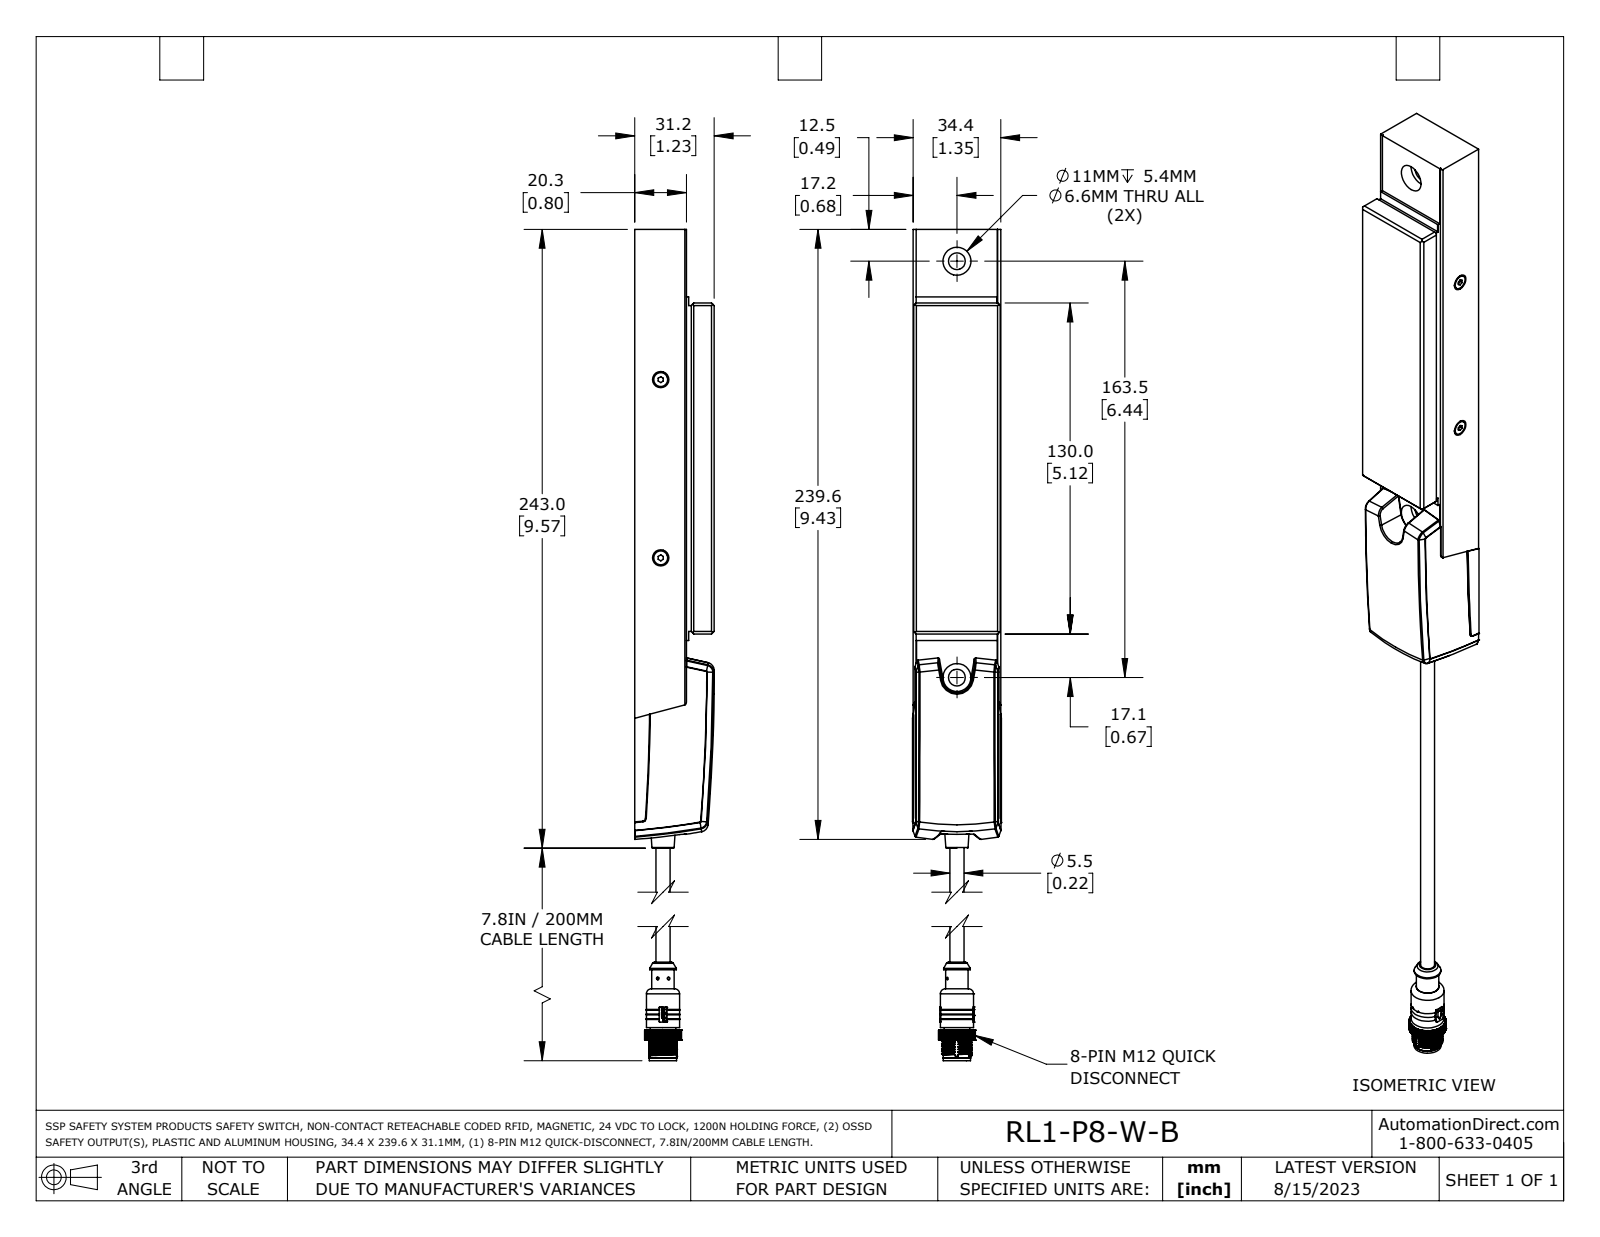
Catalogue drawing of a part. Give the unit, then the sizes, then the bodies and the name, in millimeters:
Units: millimetres
Overall size (bounding box): 434.1 × 34.9 × 31.2
Round holes (diameter × count): ⌀1 ×2, ⌀6.6 ×2, ⌀11 ×2, ⌀2.9 ×1, ⌀8.3 ×1
Round bosses / shafts (diameter × count): ⌀0.8 ×8, ⌀5.5 ×5, ⌀13 ×1, ⌀10.7 ×1, ⌀10.7 ×1, ⌀10.5 ×1, ⌀10 ×1, ⌀9.5 ×1
Partial cylindrical surfaces — rounded edges, fillets, slot ends (radius × count): R0.2 ×9, R0.2 ×4, R0.2 ×3, R0.6 ×3, R800 ×2, R1 ×1, R1.5 ×1, R7.2 ×1
Main face-to-face distances: 31.2, 34.4, 34.2, 11, 20.2, 34, 1, 0.5, 34.4, 34.6
Hole centre spacings: 4.3, 9.3, 163.5, 172.8
Volume: 237 600 mm³ · Surface area: 39 410 mm²
Bodies: 1 solid, 1030 faces (622 planar, 141 cylindrical, 267 other)
Part name (STEP PRODUCT): RL1-P8-S-B_REV2
STEP written by: SolidWorks 2021 (AUTOMOTIVE_DESIGN)
